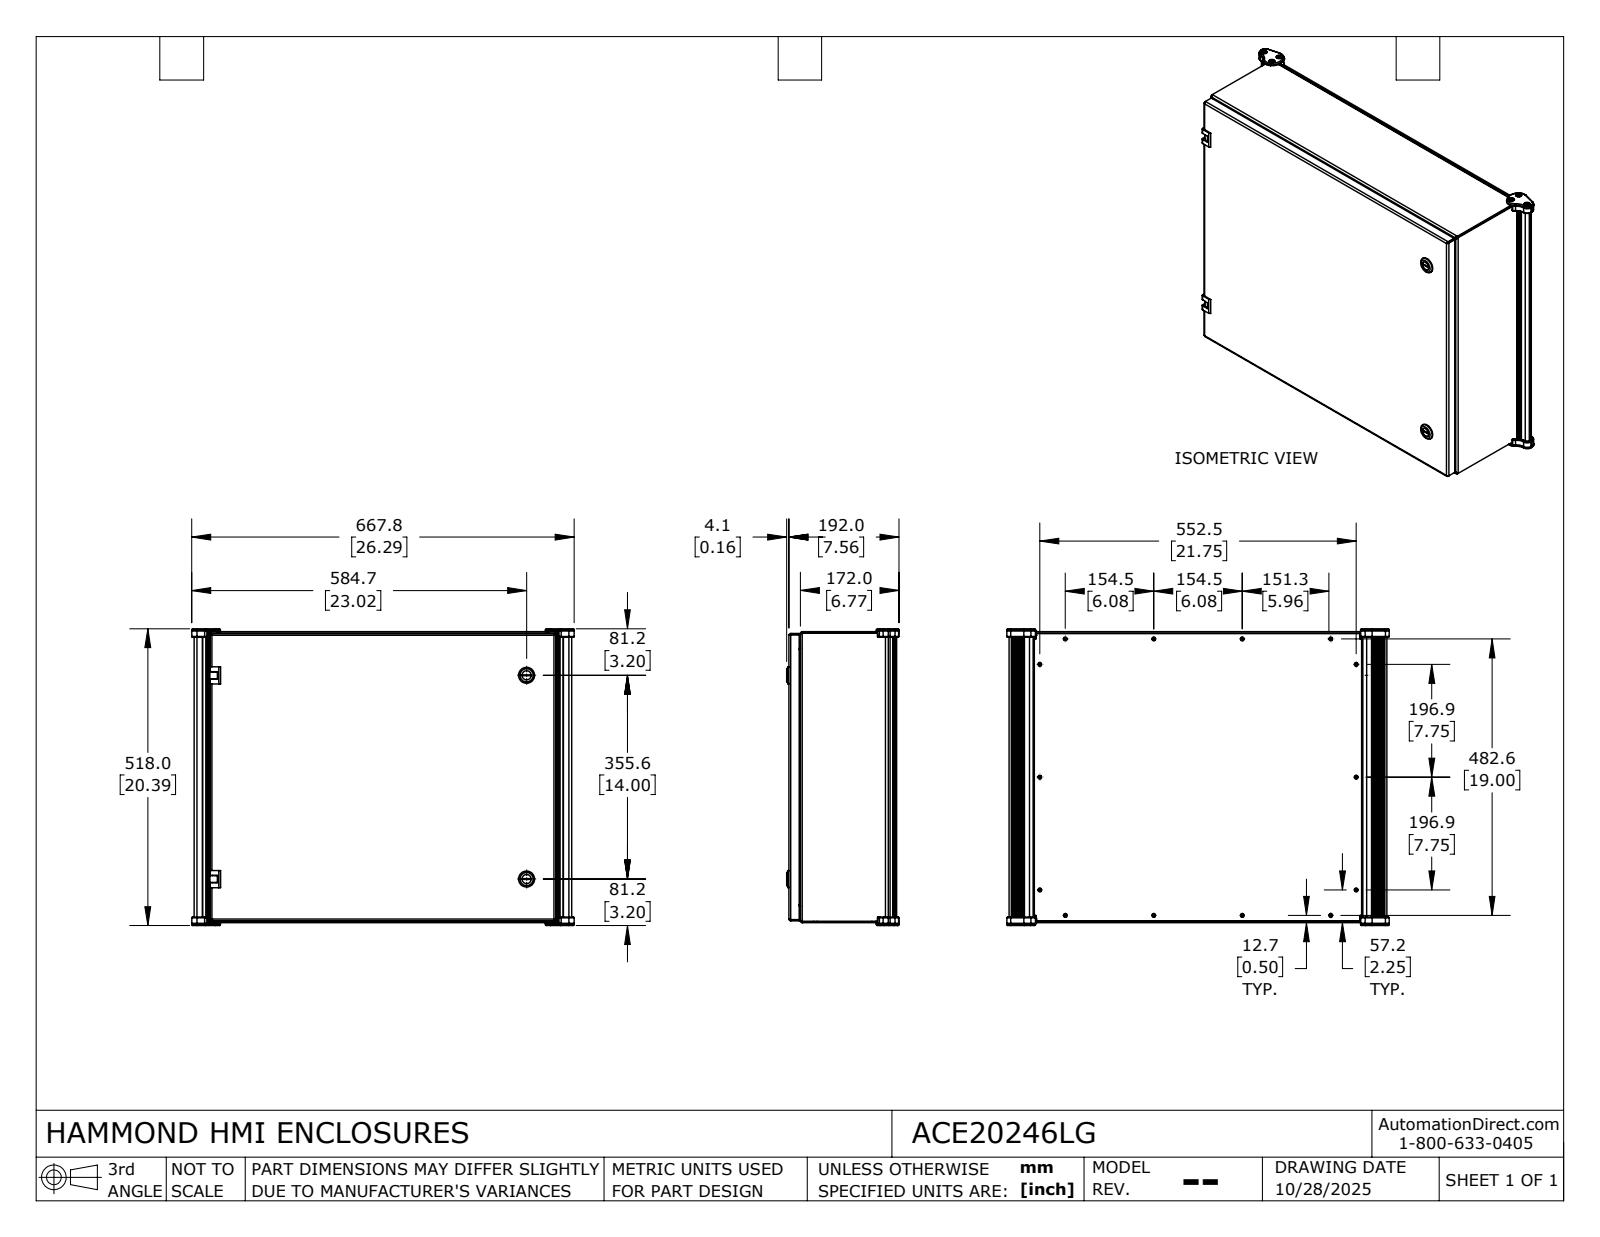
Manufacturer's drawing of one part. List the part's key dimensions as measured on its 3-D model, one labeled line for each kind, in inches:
Part name (STEP PRODUCT): ACE20246LG
STEP written by: SolidWorks 2024 (AUTOMOTIVE_DESIGN)
Units: inches
Bodies: 103 solids, 2572 faces (1232 planar, 875 cylindrical, 465 other)
Overall size (bounding box): 26.292 × 20.395 × 7.719
Volume: 203.5 in³ · Surface area: 4 462 in²
Round holes (diameter × count): ⌀0.156 ×16, ⌀0.234 ×16, ⌀0.19 ×14, ⌀0.205 ×6, ⌀0.413 ×6, ⌀0.196 ×5, ⌀0.159 ×4, ⌀0.406 ×4, ⌀0.16 ×2, ⌀0.197 ×2, ⌀0.232 ×2, ⌀0.25 ×2
Round bosses / shafts (diameter × count): ⌀0.256 ×14, ⌀0.25 ×6, ⌀0.19 ×6, ⌀0.149 ×6, ⌀0.236 ×5, ⌀0.375 ×4, ⌀0.33 ×4, ⌀1.1 ×2
Partial cylindrical surfaces — rounded edges, fillets, slot ends (radius × count): R0.01 ×38, R0.059 ×30, R0.041 ×20, R0.122 ×20, R0.016 ×16, R0.03 ×16, R0.05 ×16, R0.039 ×14
Main face-to-face distances: 0.081, 0.125, 6.831, 6.912, 6.956, 7.037, 0.206, 0.081, 23.919, 6.706
Hole centre spacings: 6.083, 19.95, 4, 2.475, 7.75, 8.026, 9.66, 10.873
